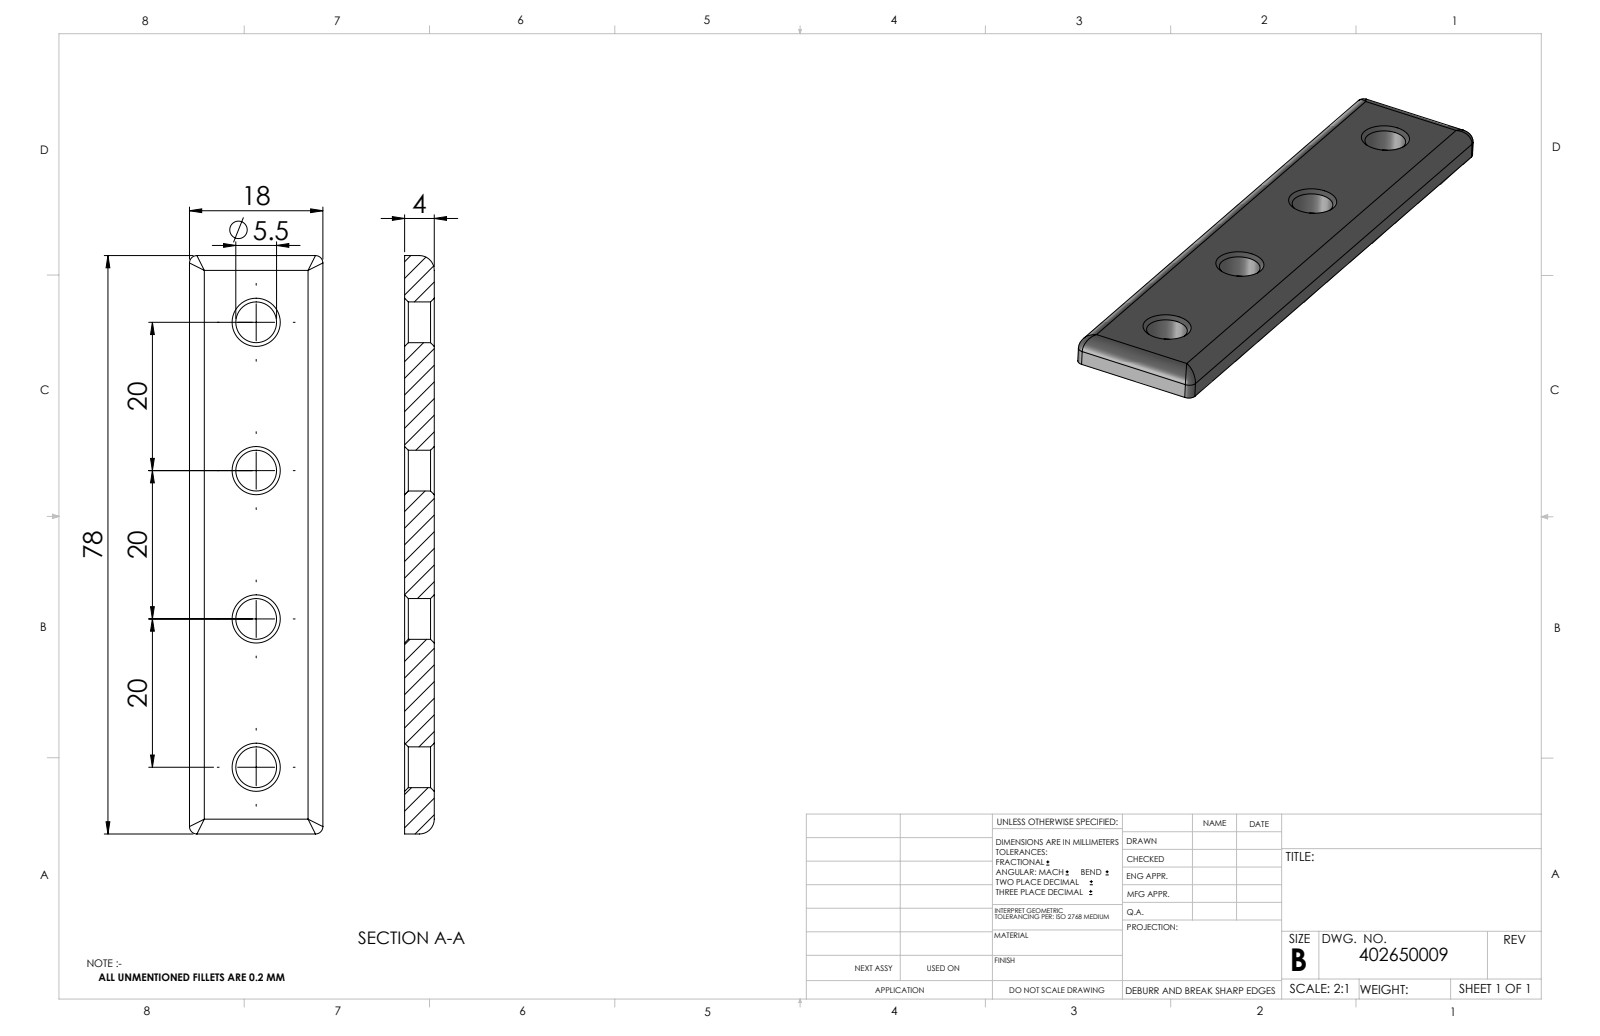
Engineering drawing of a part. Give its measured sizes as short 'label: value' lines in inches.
name: 402650009_c_1
written by: SolidWorks 2014 (CONFIG_CONTROL_DESIGN)
unit: in
bodies: 1 solid, 42 faces (6 planar, 16 cylindrical, 20 other)
size: 3.071 × 0.709 × 0.157
volume: 0.308 in³; area: 5.348 in²
holes: 4× ⌀0.217
rounds: 4× R0.039, 4× R0.079
face distances: 0.157, 0.709, 3.071
hole spacings: 0.787, 1.575, 2.362
